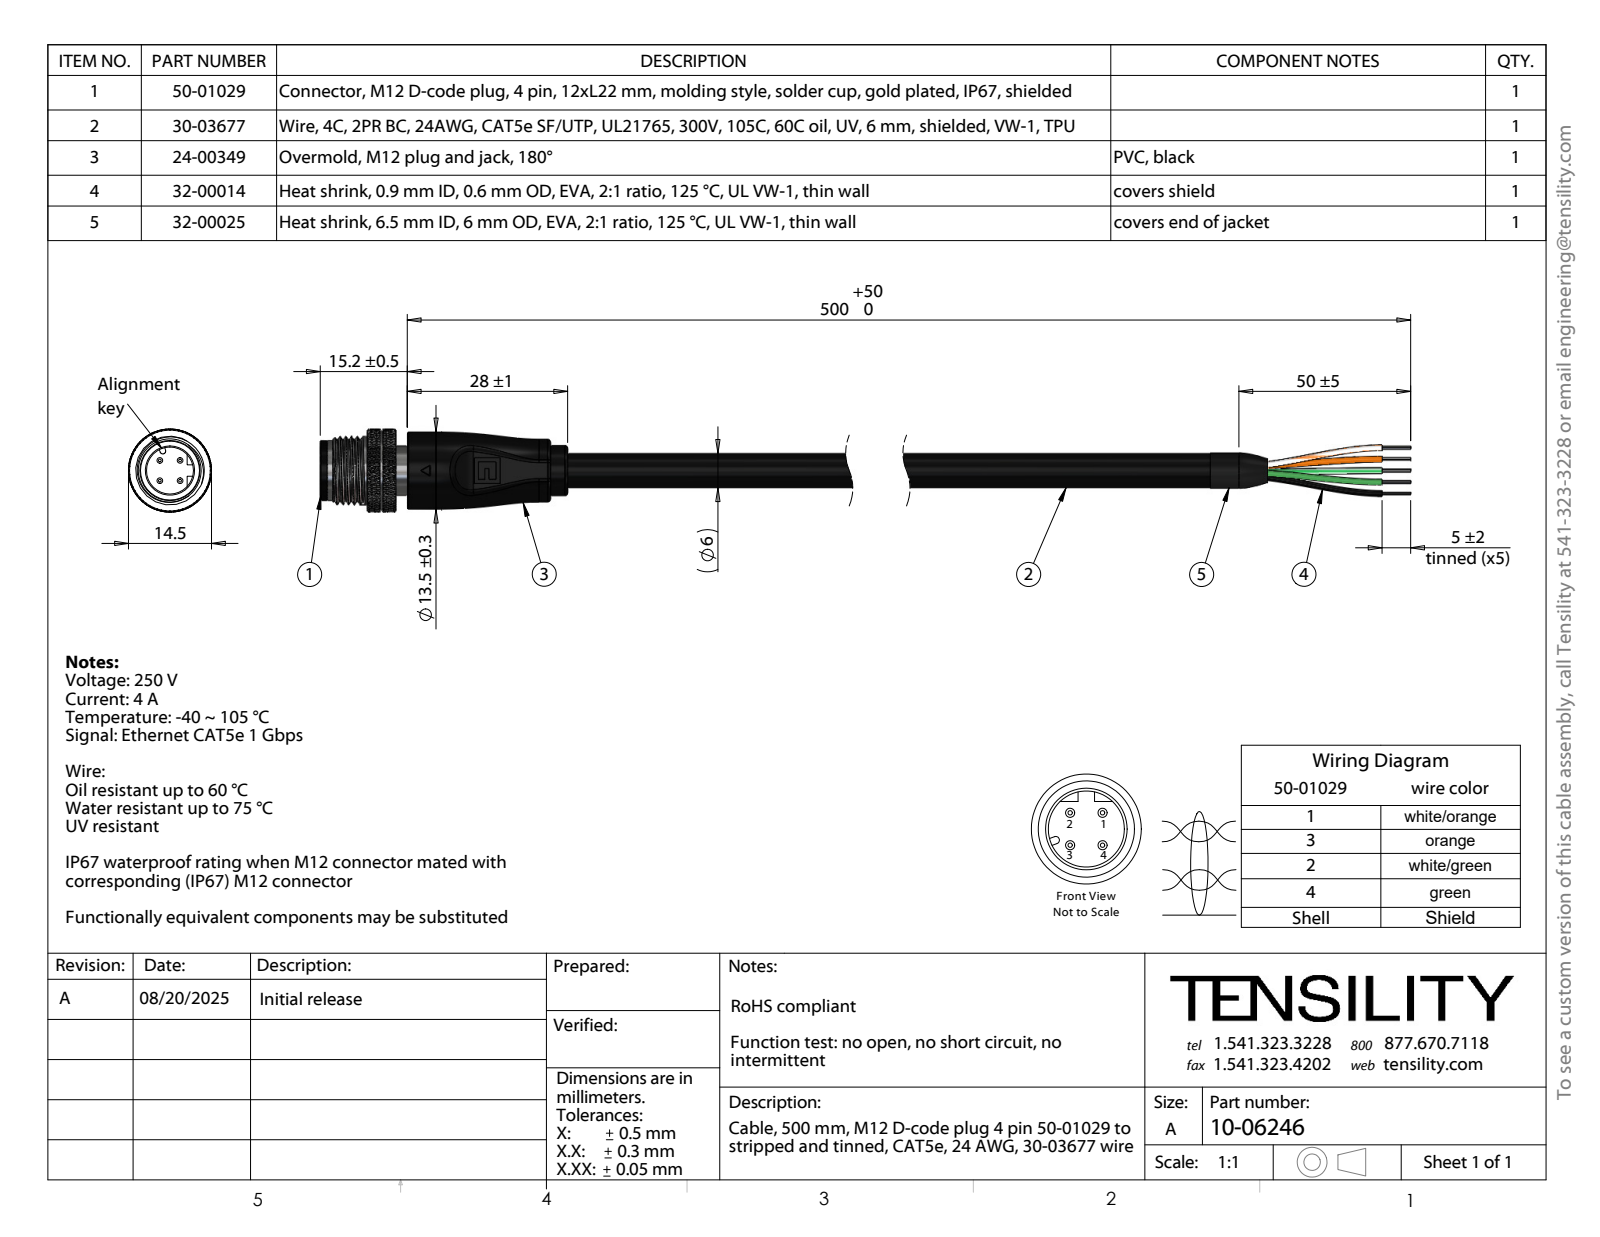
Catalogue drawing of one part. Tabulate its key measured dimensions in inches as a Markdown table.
| quantity | value |
| --- | --- |
| part name | 10-06246; 50-01029-02_默认; 24-00349_Mexico; 50-01029-04_默认 (+4 more) |
| STEP written by | SolidWorks 2025 (CONFIG_CONTROL_DESIGN) |
| units | inches |
| bodies | 86 solids, 2792 faces (263 planar, 823 cylindrical, 1706 other) |
| overall size | 8.787 × 0.571 × 0.571 |
| volume | 0.567 in³ |
| surface area | 41 in² |
| round holes (diameter × count) | 0.008 × 28, 0.039 × 4, 0.041 × 4, 0.124 × 1, 0.126 × 1, 0.132 × 1, 0.315 × 1, 0.323 × 1, 0.346 × 1, 0.374 × 1 |
| round bosses / shafts (diameter × count) | 0.008 × 35, 0.055 × 4, 0.571 × 1, 0.547 × 1, 0.531 × 1, 0.472 × 1, 0.433 × 1, 0.413 × 1 |
| partial cylindrical surfaces (radius × count) | 0.02 × 2, 0.059 × 2, 0.077 × 2, 0.197 × 1, 0.22 × 1, 0.266 × 1 |
| main face-to-face distances | 7.087, 0.276, 0.079, 7.008, 0.197, 1.102, 1.181, 5.906, 0.425, 0.15 |
| hole center spacings | 0.075, 0.082, 0.042, 0.014, 0.035, 0.043, 0.049, 0.067 |
